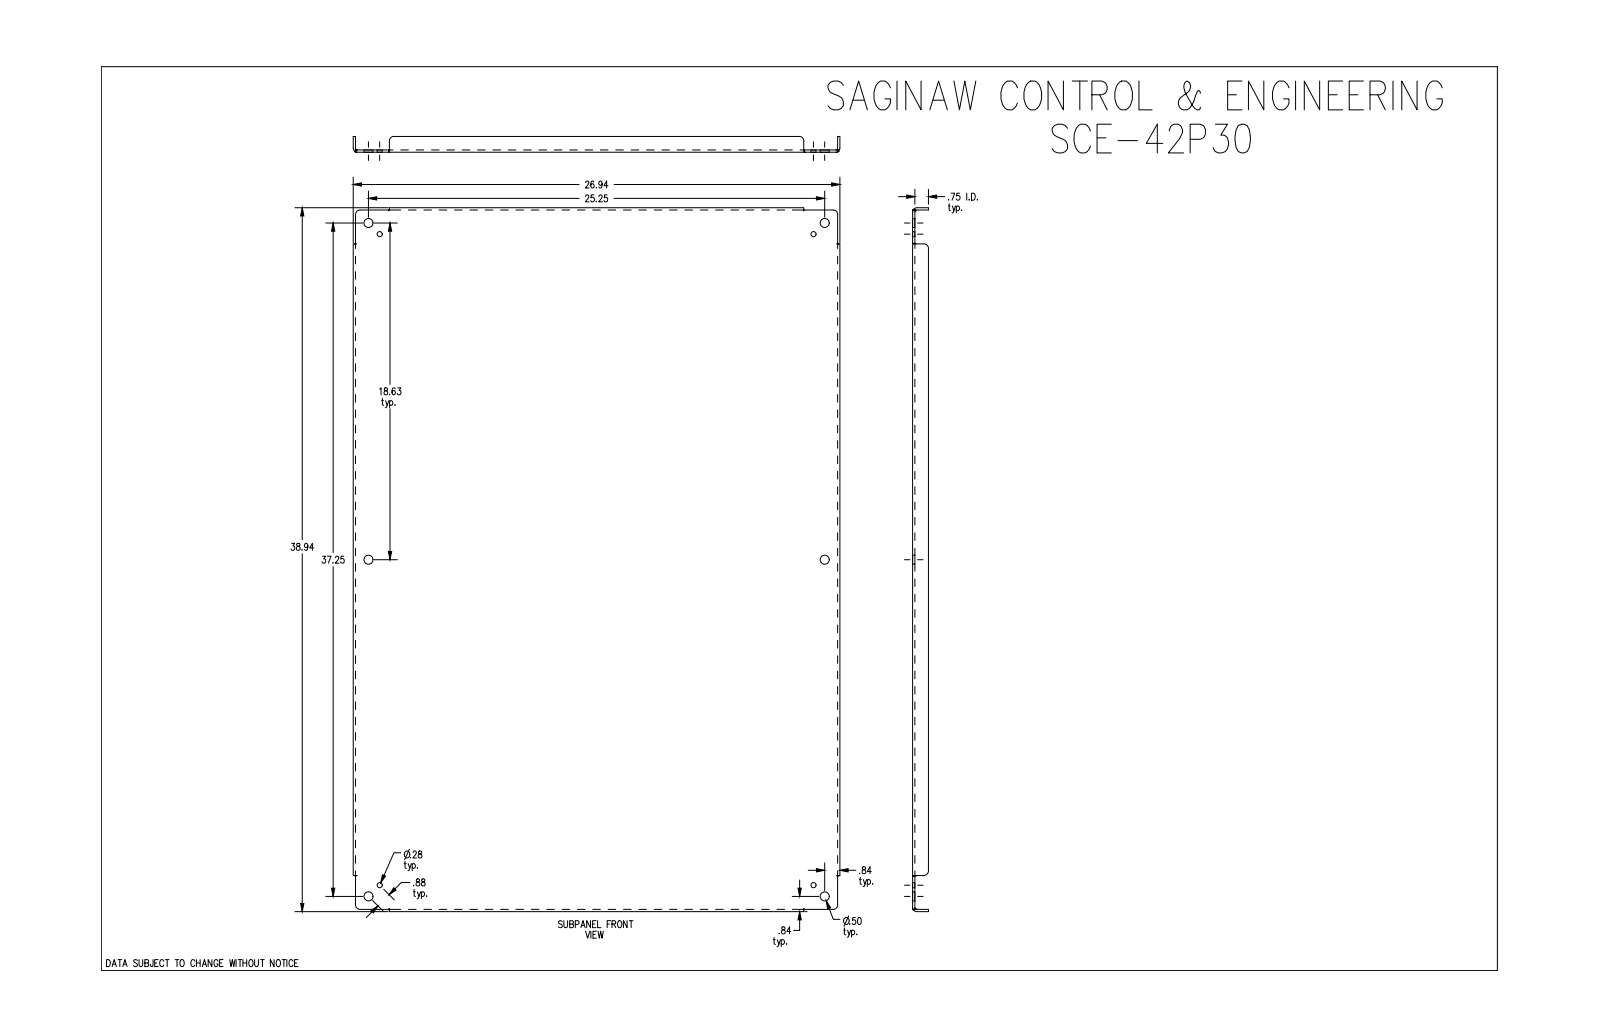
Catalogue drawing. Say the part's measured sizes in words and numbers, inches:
The part is named "SCE-42P30". Its 3-D file was written by "SolidWorks 2019 (CONFIG_CONTROL_DESIGN)". It is 1 solid with 84 faces: 30 planar, 30 cylindrical and 24 other. Overall it measures 38.938 by 26.938 by 0.875 inches. Its volume is 140.4 cubic inches and its surface area 2 266 square inches. Round holes: 6 of diameter 0.5, 4 of diameter 0.281. Partial cylindrical surfaces (rounded edges, fillets, slot ends): 8 of radius 0.25, 4 of radius 0.112, 4 of radius 0.237. The main face-to-face distances are 0.125, 0.125, 26.813, 38.813, 26.687, 26.938, 38.687, 38.938, 0.75, 0.875. The hole center spacings are 0.875, 18.017, 18.625, 24.639, 30.511, 31.376, 36.636, 44.142.
